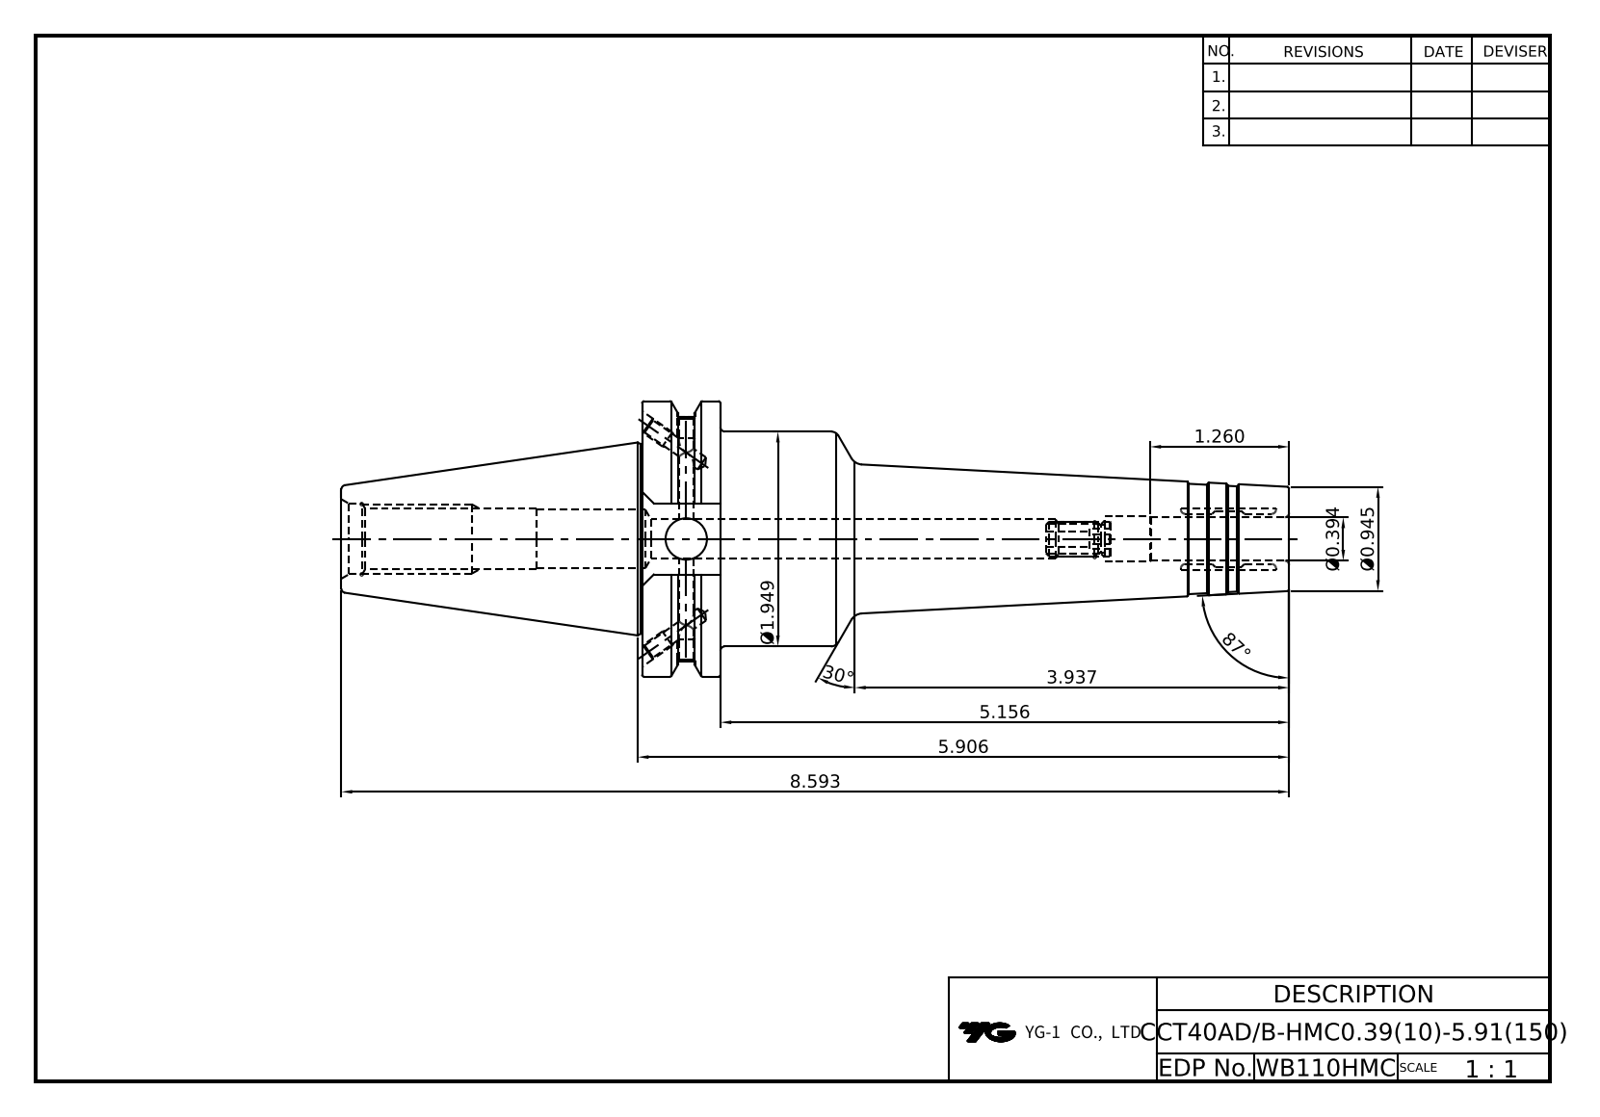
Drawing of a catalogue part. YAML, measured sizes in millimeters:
part_name: "LO-CCT40ADB-HMC10-150"
step_written_by: "Autodesk Inventor 2022 (AUTOMOTIVE_DESIGN)"
units: millimeters
bodies: {solids: 1, faces: 108, planar: 35, cylindrical: 31, other: 42}
overall_size: [218.25, 63.5, 61.09]
volume: 220921
surface_area: 37661
round_holes:
  - {diameter: 3.24, count: 4}
  - {diameter: 4, count: 2}
  - {diameter: 4.2, count: 2}
  - {diameter: 6.92, count: 1}
  - {diameter: 9, count: 1}
  - {diameter: 9.53, count: 1}
  - {diameter: 10, count: 1}
  - {diameter: 10.6, count: 1}
  - {diameter: 13, count: 1}
  - {diameter: 13.39, count: 1}
  - {diameter: 16.3, count: 1}
round_bosses_or_shafts:
  - {diameter: 63.5, count: 1}
  - {diameter: 49.5, count: 1}
  - {diameter: 43.8, count: 1}
partial_cylinders:
  - {radius: 8.19, count: 1}
  - {radius: 28.15, count: 1}
face_to_face_distances: [18.05, 149, 130.95, 47.6, 16.38, 69.25, 87.3, 218.25, 81.34, 12.09]
